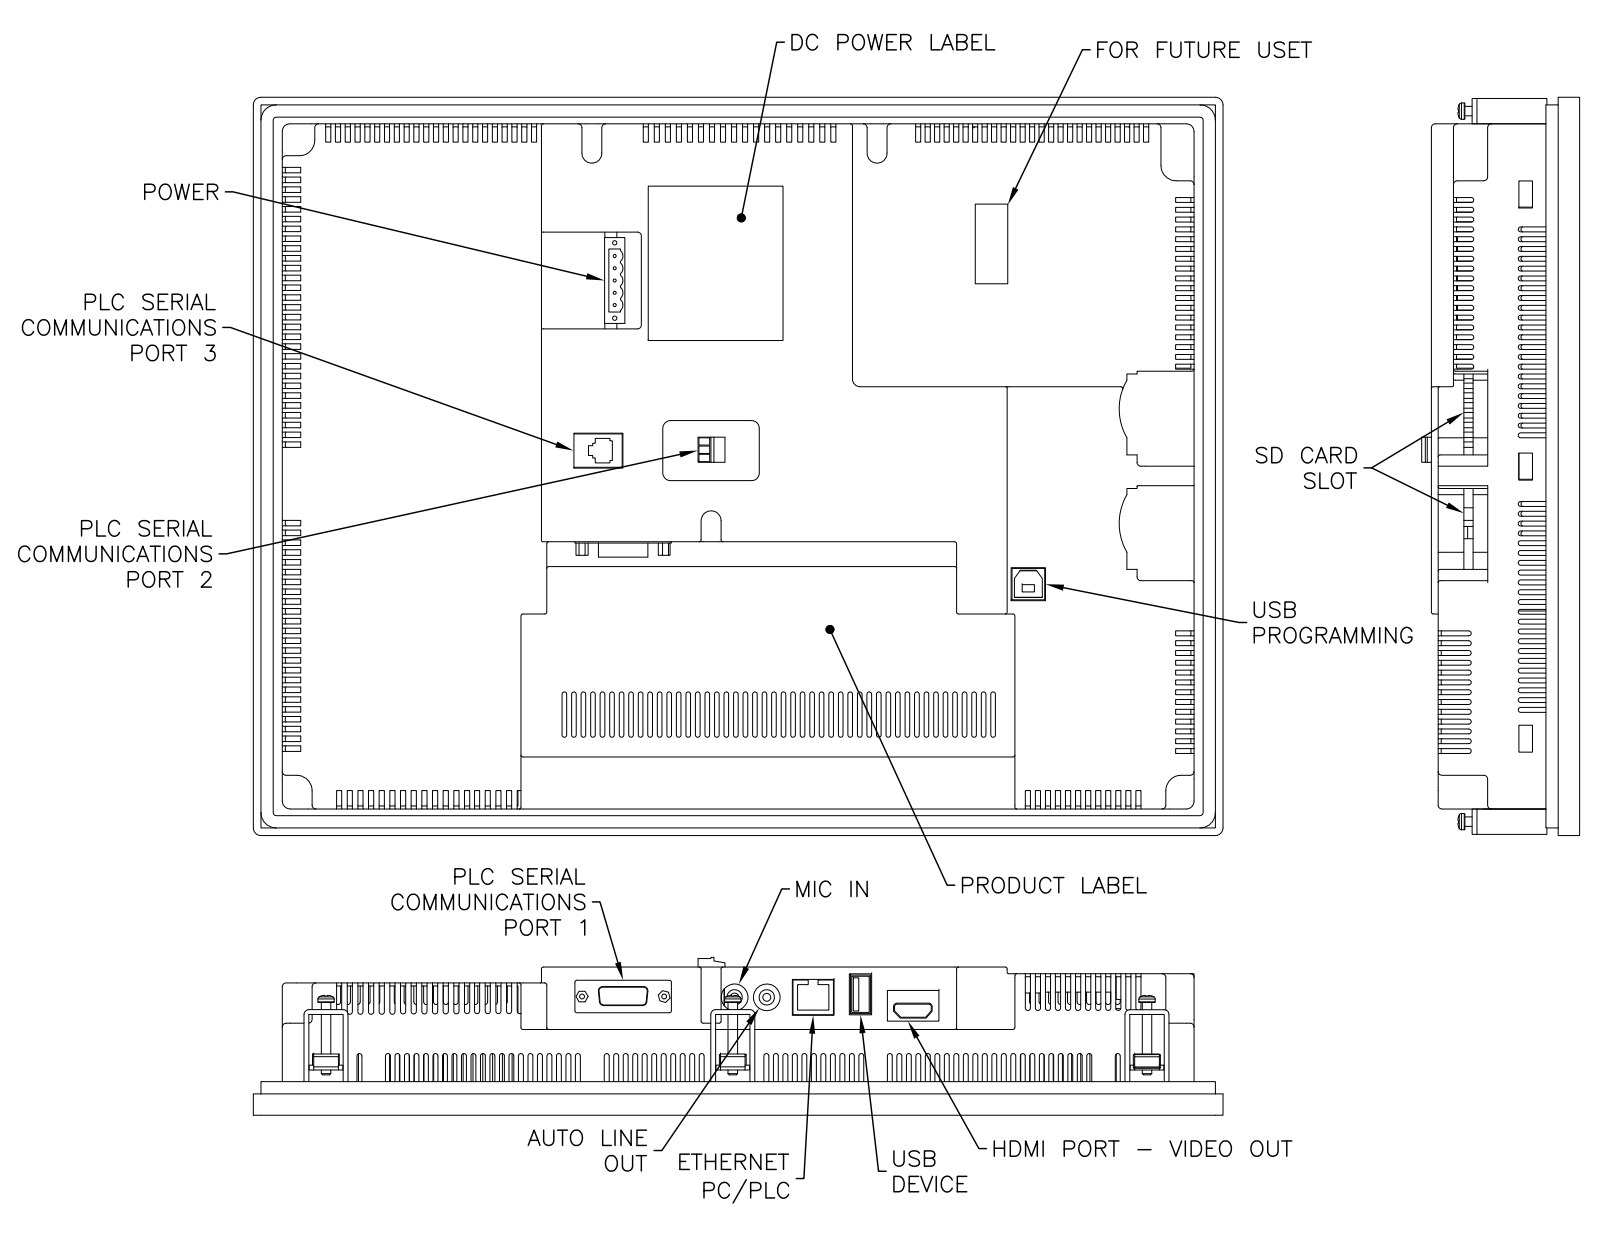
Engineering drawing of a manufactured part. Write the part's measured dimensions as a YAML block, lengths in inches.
part_name: "EA9-T15CL"
step_written_by: "SolidWorks 2014 (AUTOMOTIVE_DESIGN)"
units: inches
bodies: {solids: 4, faces: 3212, planar: 1676, cylindrical: 1434, other: 102}
overall_size: [15.827, 12.047, 2.578]
volume: 66.29
surface_area: 1139
round_holes:
  - {diameter: 0.07, count: 2}
  - {diameter: 0.08, count: 2}
  - {diameter: 0.435, count: 2}
  - {diameter: 0.13, count: 1}
  - {diameter: 0.14, count: 1}
round_bosses_or_shafts:
  - {diameter: 0.05, count: 5}
  - {diameter: 0.25, count: 2}
partial_cylinders:
  - {radius: 0.04, count: 395}
  - {radius: 0.042, count: 95}
  - {radius: 0.038, count: 92}
  - {radius: 0.043, count: 88}
  - {radius: 0.031, count: 66}
  - {radius: 0.045, count: 53}
  - {radius: 0.062, count: 49}
  - {radius: 0.02, count: 20}
face_to_face_distances: [0.05, 2.109, 0.1, 0.26, 2.369, 2.059, 0.099, 0.2, 0.15, 0.049]
hole_center_spacings: [0.525, 1.15, 1.23, 1.34, 1.675, 2.49, 3.015]
